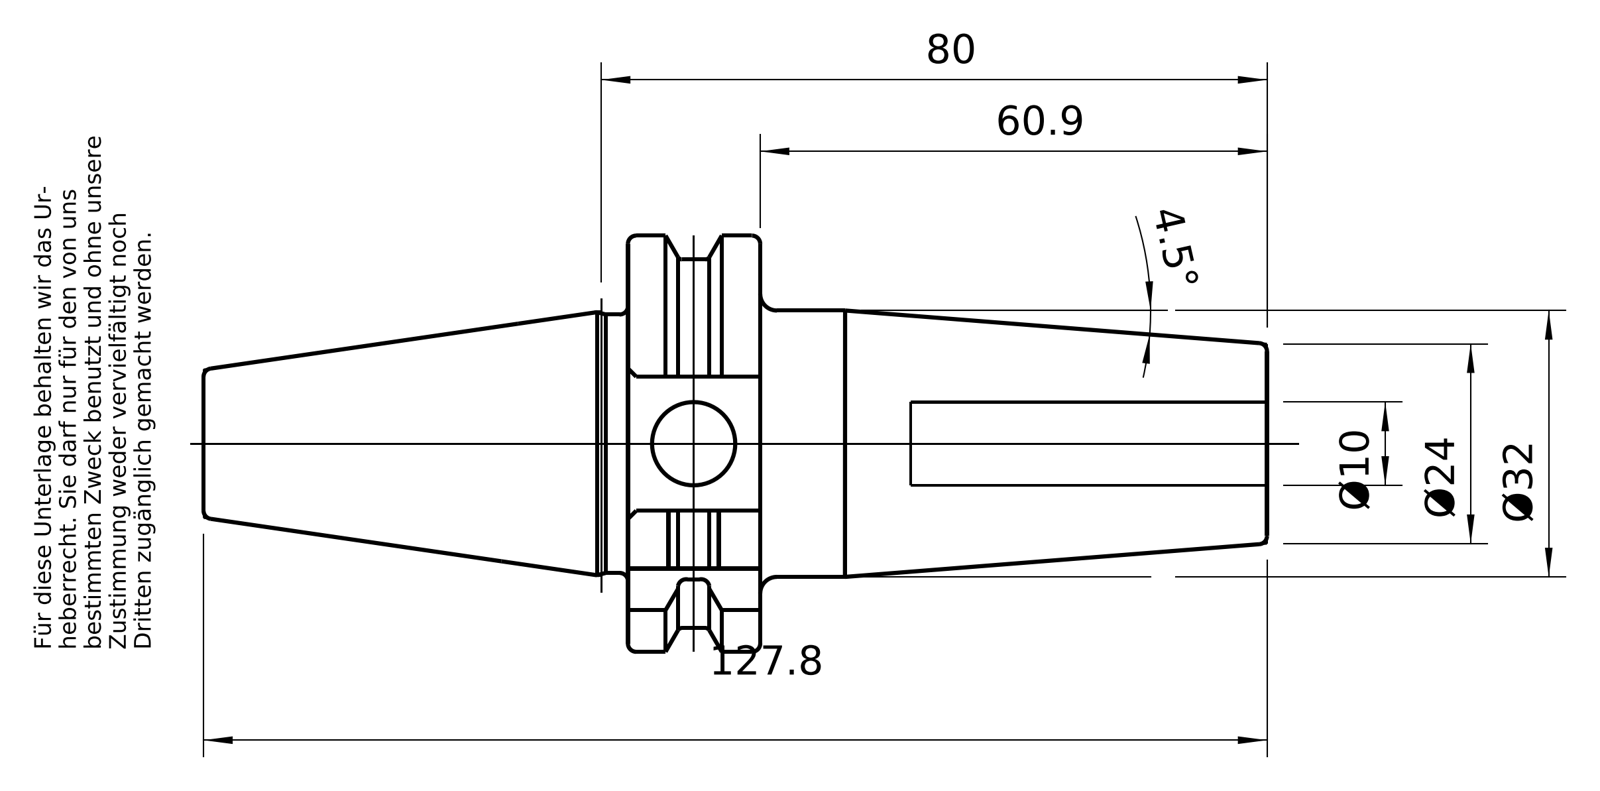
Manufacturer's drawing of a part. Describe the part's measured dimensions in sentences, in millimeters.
The part is named "30-440-10". Its 3-D file was written by "PRO/ENGINEER BY PARAMETRIC TECHNOLOGY CORPORATION, 2010430 (CONFIG_CONTROL_DESIGN)". It is 1 solid with 92 faces: 21 planar, 23 cylindrical and 48 other. Overall it measures 127.65 by 49.98 by 47.32 millimeters. Its volume is 84 833 cubic millimeters and its surface area 18 252 square millimeters. Round holes: 1 of diameter 10, 1 of diameter 10.11, 1 of diameter 13.01, 1 of diameter 13.5. Round bosses or shafts: 1 of diameter 32, 1 of diameter 31.05, 1 of diameter 12.01. Partial cylindrical surfaces (rounded edges, fillets, slot ends): 1 of radius 22.02, 1 of radius 24.99. The main face-to-face distances are 15.85, 60.95, 76.8, 35.1, 16.1, 34.8, 18.95, 42, 6.95, 23.05.
